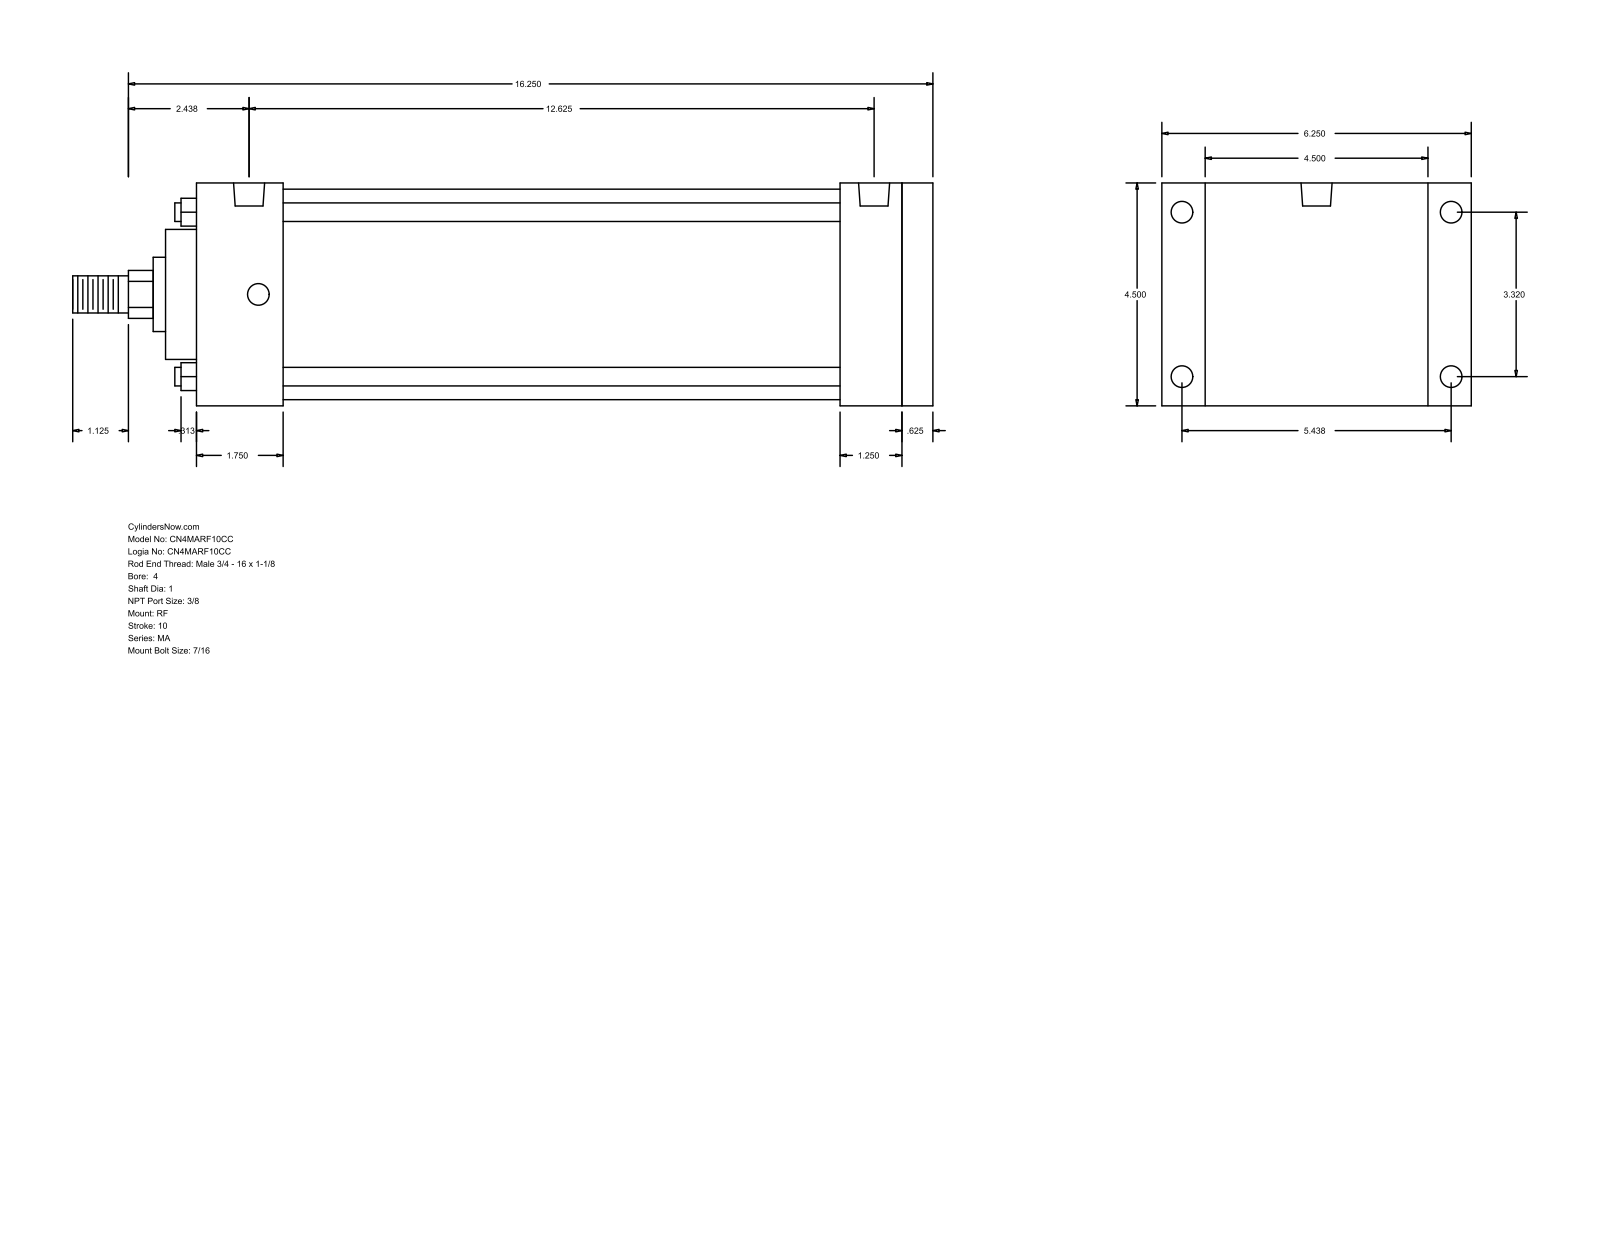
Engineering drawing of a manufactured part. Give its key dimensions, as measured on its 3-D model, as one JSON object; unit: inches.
{"part_name": "MA_RF__0400_1", "step_written_by": "GSSL Pune (CONFIG_CONTROL_DESIGN)", "units": "inches", "bodies": {"solids": 0, "faces": 94, "planar": 65, "cylindrical": 29, "other": 0}, "overall_size": [17.375, 6.25, 4.5], "round_holes": [[0.437, 8], [0.627, 2]], "round_bosses_or_shafts": [[0.375, 4], [4.25, 1], [2.625, 1], [1.5, 1], [1, 1], [0.75, 1]], "partial_cylinders_radius": [[0.484, 1]], "face_to_face_distances": [4.5, 14.875, 0.625, 14.25, 0.875, 5.375, 13, 1.25, 1.875, 1.75], "hole_center_spacings": [3.32, 5.438, 6.371, 12.25, 0.187, 0.188, 12.437, 12.438]}
